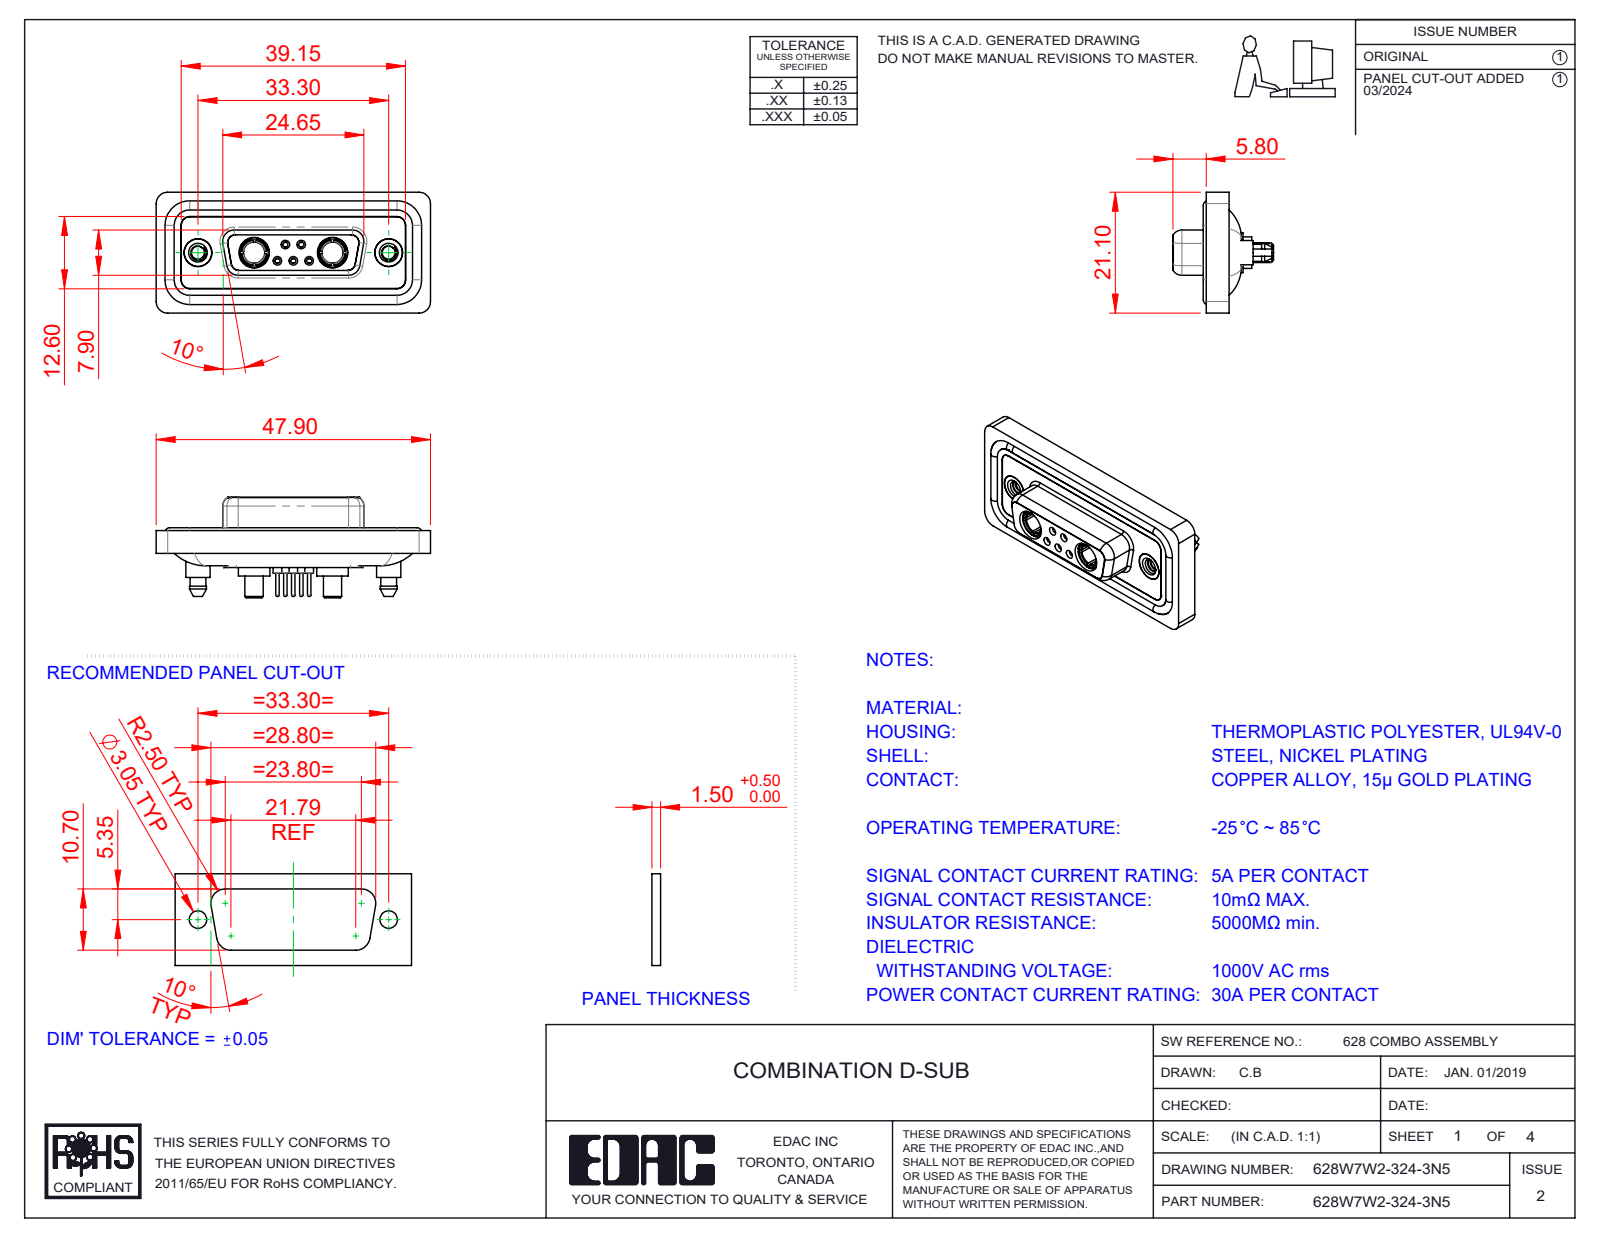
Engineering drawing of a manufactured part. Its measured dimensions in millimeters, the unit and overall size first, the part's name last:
Units: millimetres
Overall size (bounding box): 47.9 × 21.1 × 17.55
Round holes (diameter × count): ⌀0.9 ×5, ⌀1.1 ×5, ⌀1.5 ×5, ⌀2 ×5, ⌀4.85 ×4, ⌀1.6 ×3, ⌀1.7 ×2, ⌀2.26 ×2, ⌀3.7 ×2, ⌀4 ×2, ⌀4.05 ×2, ⌀5 ×2
Round bosses / shafts (diameter × count): ⌀1.6 ×6, ⌀2.2 ×5, ⌀0.6 ×5, ⌀5.5 ×2, ⌀5.4 ×2, ⌀5.2 ×2, ⌀4.96 ×2, ⌀4.95 ×2
Partial cylindrical surfaces — rounded edges, fillets, slot ends (radius × count): R1.5 ×24, R2 ×20, R1.35 ×12, R1.6 ×10, R0.25 ×4, R0.5 ×4, R0.6 ×4, R0.65 ×4
Main face-to-face distances: 0.4, 1.8, 1.6, 0.5, 2.9, 1.1, 7.45, 5.65, 6.6, 7.05
Hole centre spacings: 3.16, 2.77, 9.8, 23.5, 4.31, 4.33, 5.03, 5.04
Volume: 6 225 mm³ · Surface area: 10 227 mm²
Bodies: 16 solids, 859 faces (254 planar, 361 cylindrical, 244 other)
Part name (STEP PRODUCT): 628Combo Housing_7W2; Power Socket_30A S; 628Combo Threaded Boardlock_5; 628Combo Contact Row 1_24 (+5 more)
STEP written by: SolidWorks 2023 (CONFIG_CONTROL_DESIGN)
